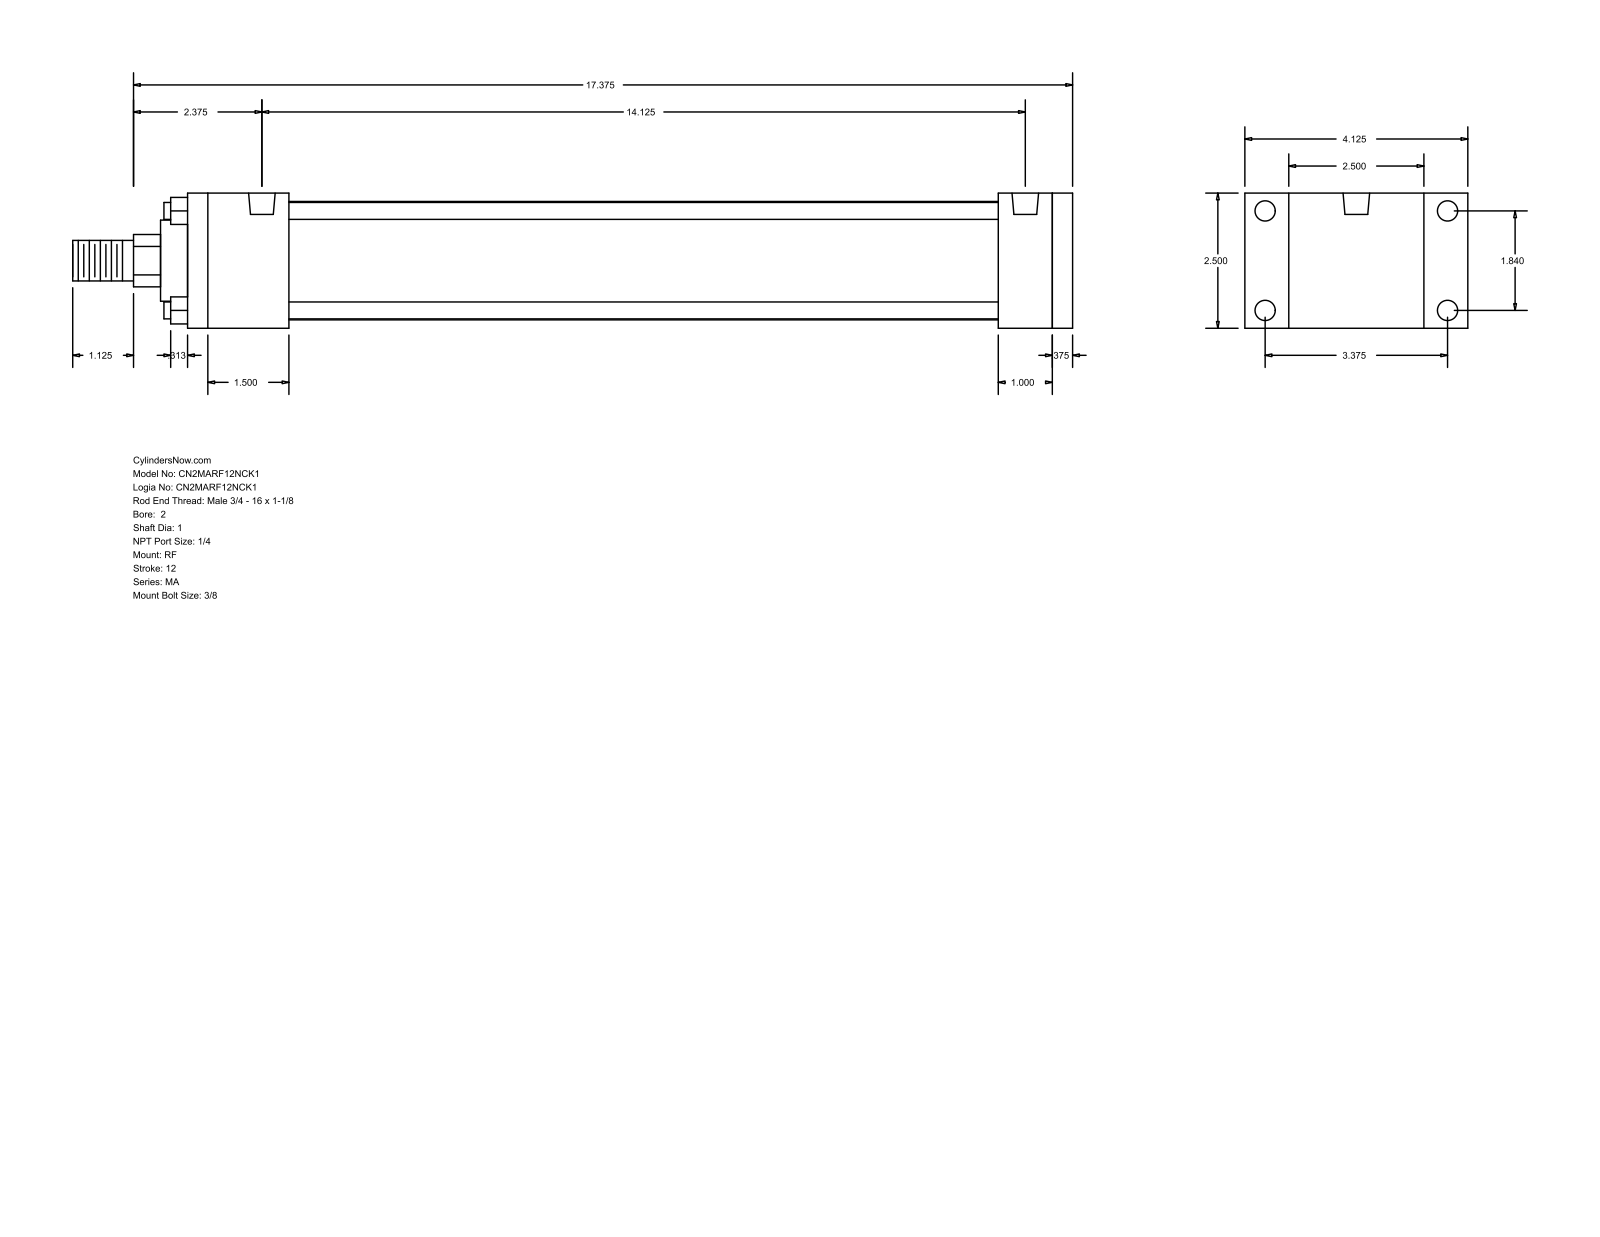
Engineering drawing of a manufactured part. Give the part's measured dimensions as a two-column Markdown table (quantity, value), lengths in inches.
| quantity | value |
| --- | --- |
| part name | MA_RF__0200_1 |
| STEP written by | GSSL Pune (CONFIG_CONTROL_DESIGN) |
| units | inches |
| bodies | 0 solids, 92 faces (64 planar, 28 cylindrical, 0 other) |
| overall size | 18.5 × 4.125 × 2.5 |
| round holes (diameter × count) | 0.313 × 4, 0.375 × 4, 0.492 × 2 |
| round bosses / shafts (diameter × count) | 0.313 × 4, 2.19 × 1, 1.5 × 1, 1 × 1, 0.75 × 1 |
| partial cylindrical surfaces (radius × count) | 0.484 × 1 |
| main face-to-face distances | 2.5, 16, 0.375, 16.375, 1, 0.813, 0.5, 1.875, 14.125, 14.5 |
| hole center spacings | 1.84, 3.375, 3.844, 14.125 |
